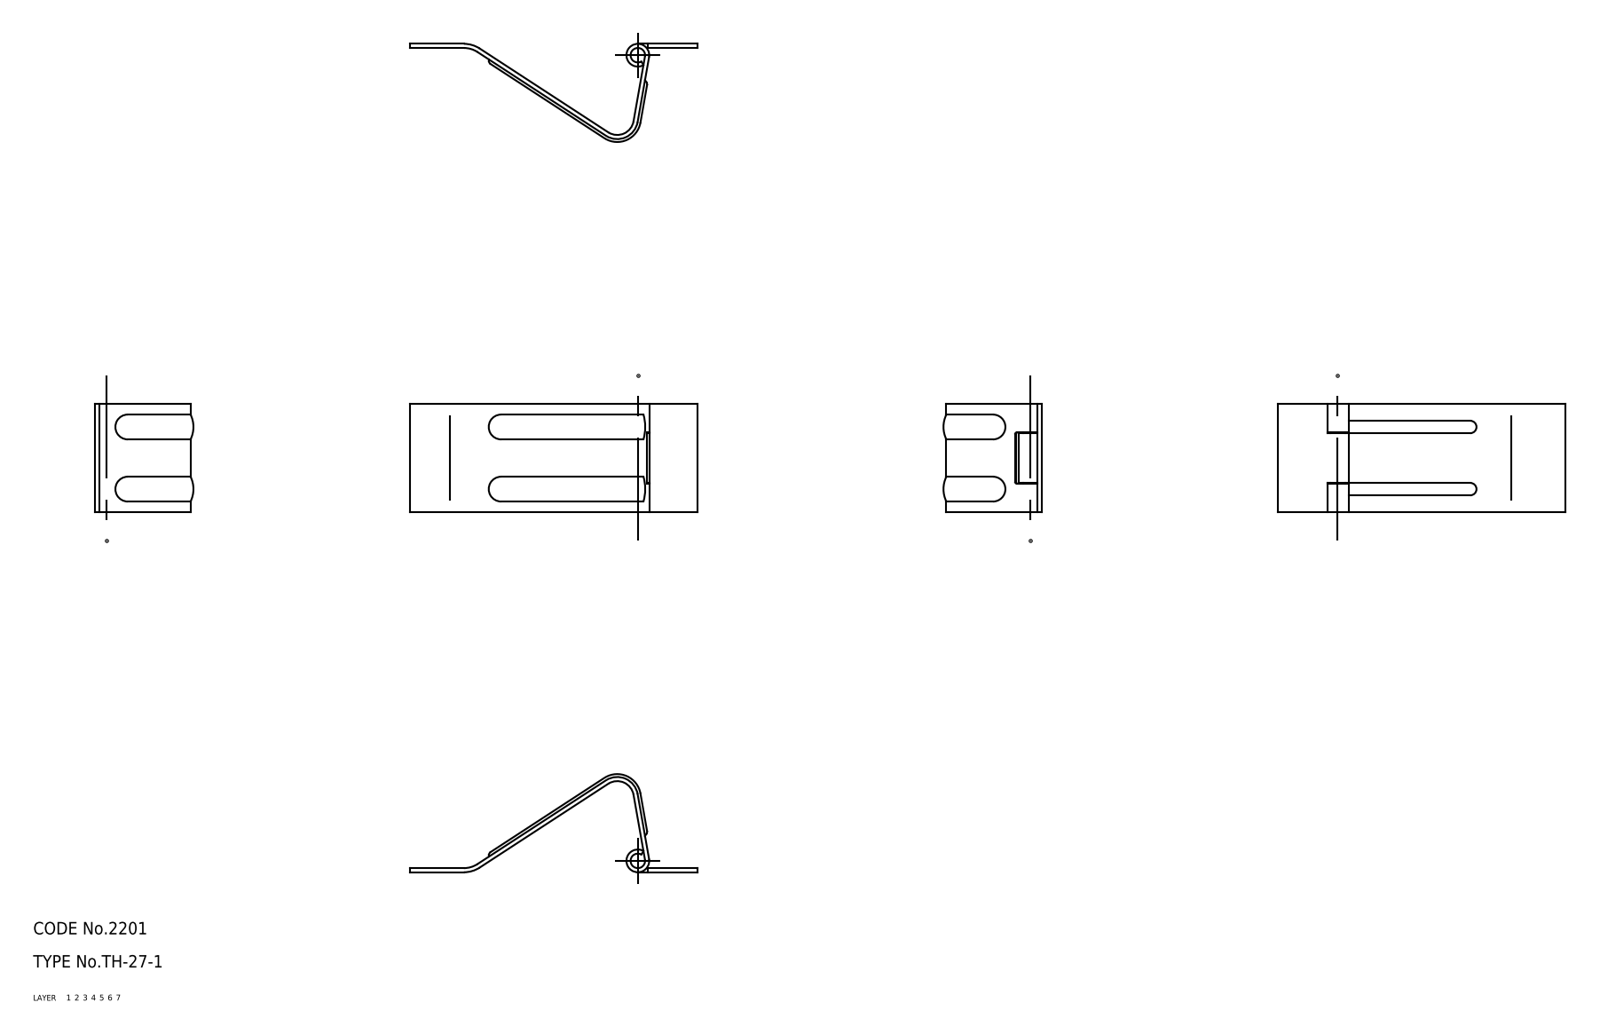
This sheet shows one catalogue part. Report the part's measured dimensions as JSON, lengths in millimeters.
{"part_name": "shaft; hinge piece_B; hinge piece_A; TH_27_1_6652_36", "step_written_by": "CADfix (AUTOMOTIVE_DESIGN)", "units": "millimeters", "bodies": {"solids": 3, "faces": 64, "planar": 0, "cylindrical": 0, "other": 64}, "overall_size": [69.5, 26, 24], "volume_mm3": 3107, "surface_area_mm2": 6230}
